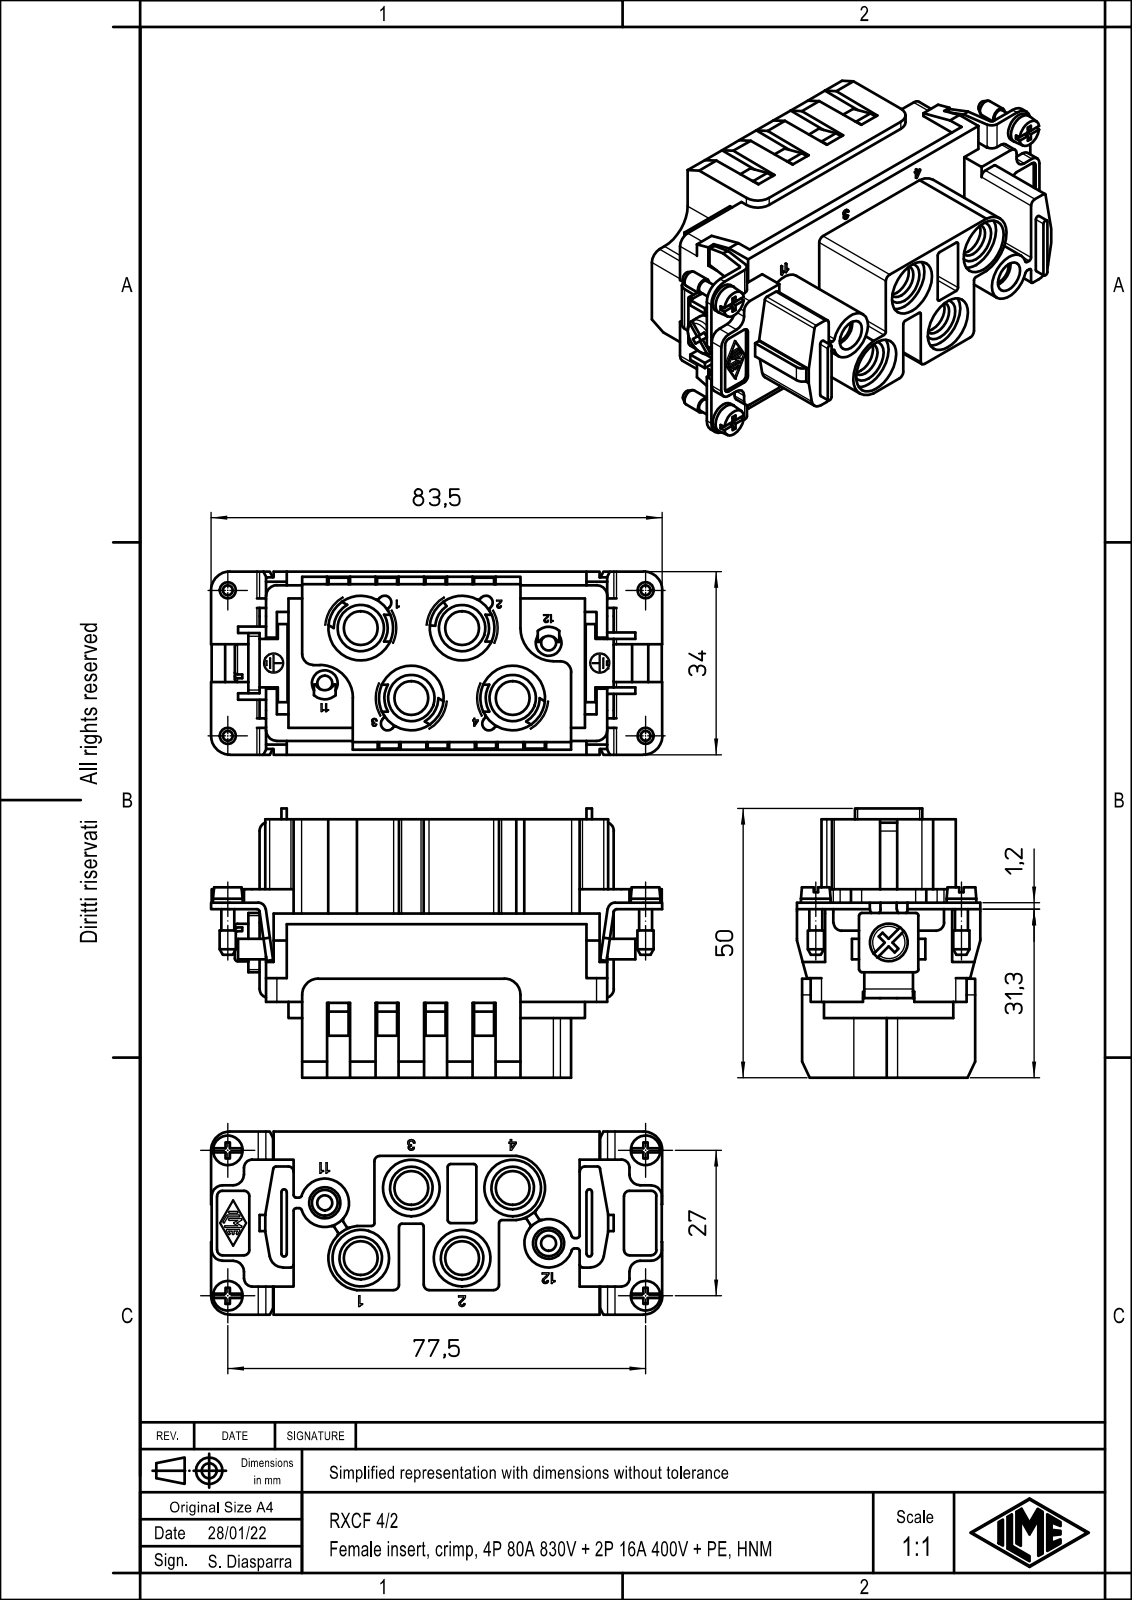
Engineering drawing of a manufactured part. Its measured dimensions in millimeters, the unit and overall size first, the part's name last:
Units: millimetres
Overall size (bounding box): 83.7 × 50 × 34
Round holes (diameter × count): ⌀6.3 ×4, ⌀8.6 ×4, ⌀10.5 ×4, ⌀12 ×4, ⌀2.8 ×2, ⌀4.8 ×2, ⌀5.8 ×2, ⌀3.3 ×1
Round bosses / shafts (diameter × count): ⌀5.5 ×4, ⌀3 ×4, ⌀2.4 ×4, ⌀9 ×2, ⌀7 ×1
Partial cylindrical surfaces — rounded edges, fillets, slot ends (radius × count): R0.5 ×38, R1 ×16, R0.17 ×15, R2 ×14, R1.5 ×6, R3 ×6, R1.25 ×4, R1.7 ×4
Main face-to-face distances: 30.5, 2, 1.6, 1.99, 26.91, 28.51, 3.59, 1.2, 17.5, 28.9
Hole centre spacings: 16.04, 12.22, 16.28, 18.8, 27.44, 34.96, 31.05, 42.17
Volume: 51 164 mm³ · Surface area: 26 795 mm²
Bodies: 1 solid, 1014 faces (769 planar, 207 cylindrical, 38 other)
Part name (STEP PRODUCT): RXCF_4-2
STEP written by: Creo Elements/Direct Modeling 20.1B 02-Apr-2019 (C) Parametric Technology GmbH (AUTOMOTIVE_DESIGN)
